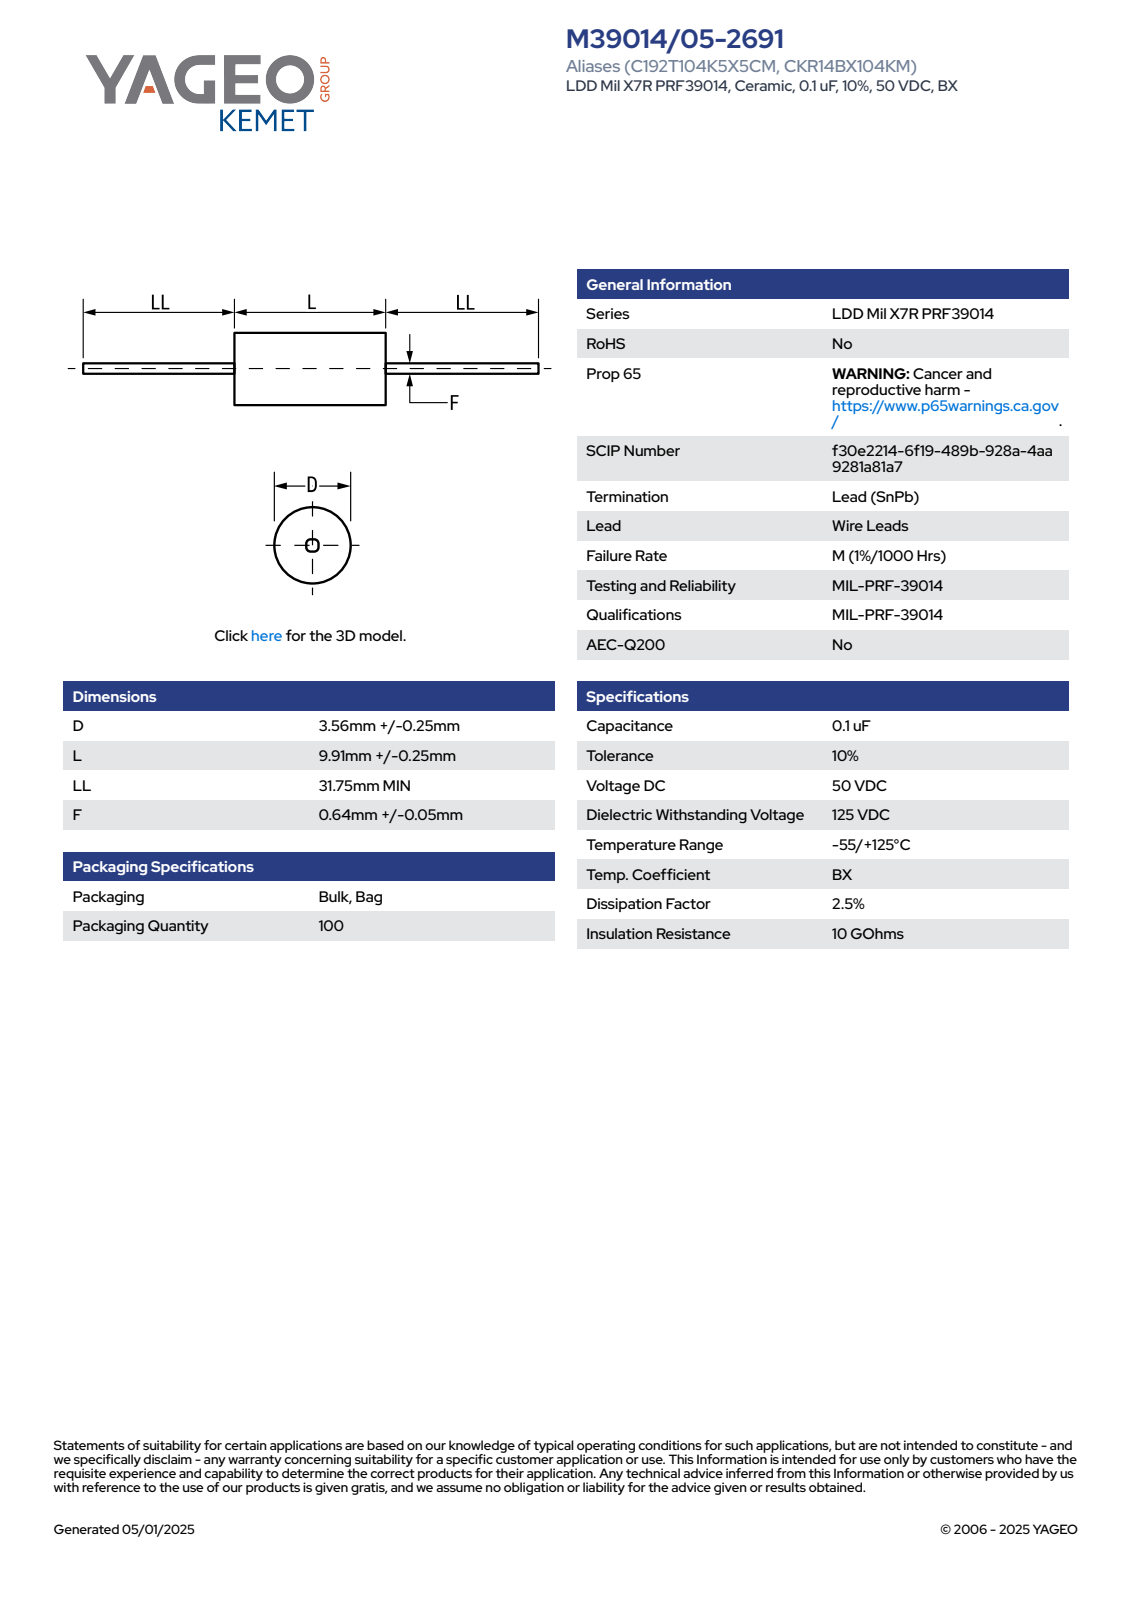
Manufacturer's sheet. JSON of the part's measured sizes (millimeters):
{"part_name": "CCA_AXM_C192_D3.81L10.16LL31.75F0.69", "step_written_by": "SolidWorks 2021 (AUTOMOTIVE_DESIGN)", "units": "millimeters", "bodies": {"solids": 1, "faces": 66, "planar": 26, "cylindrical": 9, "other": 31}, "overall_size": [73.66, 3.81, 3.81], "volume_mm3": 140, "surface_area_mm2": 282, "round_bosses_or_shafts": [[3.81, 1], [0.69, 1]], "partial_cylinders_radius": [[1.9, 1]], "face_to_face_distances": [10.16, 31.75, 41.91, 73.66]}
